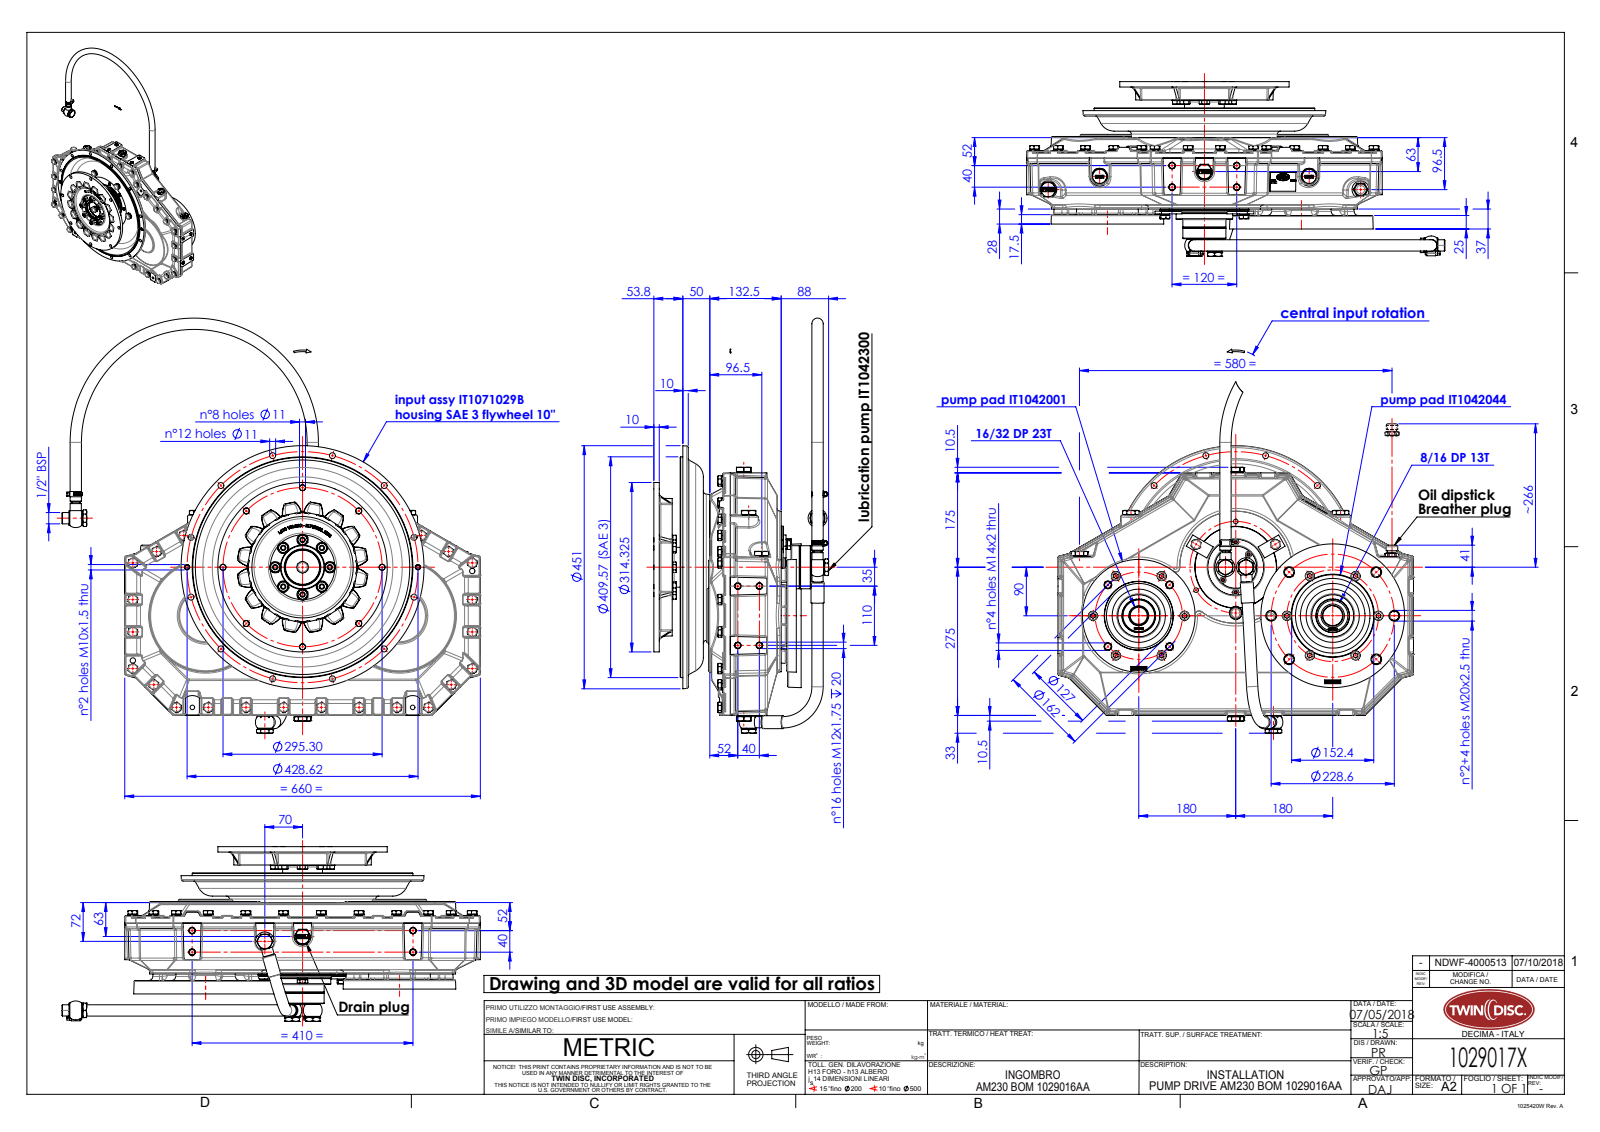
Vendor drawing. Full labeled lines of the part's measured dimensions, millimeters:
Part name (STEP PRODUCT): 1029017X; IT1042044_rev00-installation; IT1071029B-installation; IT1042300_A-installation (+6 more)
STEP written by: SolidWorks 2015 (AUTOMOTIVE_DESIGN)
Units: millimetres
Bodies: 80 solids, 9322 faces (4160 planar, 2268 cylindrical, 2894 other)
Overall size (bounding box): 776.5 × 770.2 × 324.5
Volume: 7 471 000 mm³ · Surface area: 3 449 000 mm²
Round holes (diameter × count): ⌀10.5 ×48, ⌀10.2 ×41, ⌀11 ×33, ⌀8.5 ×32, ⌀12 ×16, ⌀13 ×15, ⌀17 ×12, ⌀8 ×10, ⌀10 ×10, ⌀21 ×10, ⌀10.7 ×8, ⌀12.2 ×7
Round bosses / shafts (diameter × count): ⌀10 ×61, ⌀16.2 ×41, ⌀18.1 ×32, ⌀16 ×12, ⌀18 ×11, ⌀21 ×10, ⌀21.1 ×7, ⌀20 ×7
Partial cylindrical surfaces — rounded edges, fillets, slot ends (radius × count): R2 ×217, R3 ×147, R2.5 ×110, R5 ×90, R1 ×68, R4 ×64, R0.45 ×58, R42.91 ×32
Main face-to-face distances: 38, 37, 152.5, 40, 20, 21, 10, 94.5, 19, 5
Hole centre spacings: 120, 57.4, 75, 138.58, 40, 207.84, 22.59, 51.37
